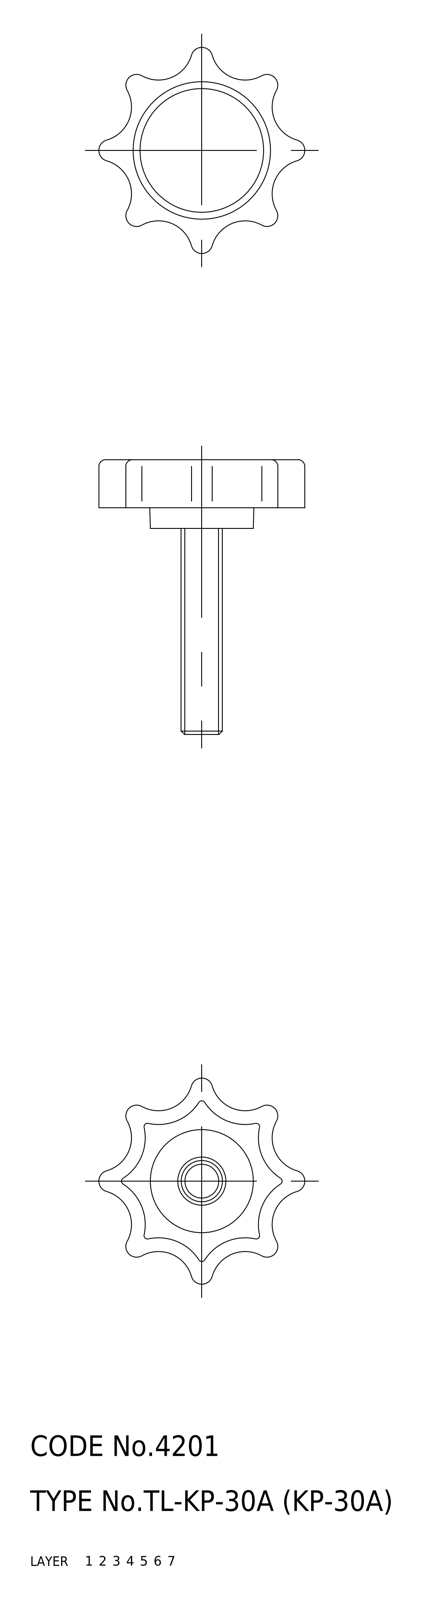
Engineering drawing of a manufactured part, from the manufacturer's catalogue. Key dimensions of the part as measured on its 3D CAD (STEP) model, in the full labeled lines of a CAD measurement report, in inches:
Part name (STEP PRODUCT): screw; knob; KP_30A_7996_36
STEP written by: CADfix (AUTOMOTIVE_DESIGN)
Units: inches
Bodies: 2 solids, 72 faces (0 planar, 0 cylindrical, 72 other)
Overall size (bounding box): 1.575 × 1.181 × 1.181
Volume: 0.272 in³ · Surface area: 5.089 in²
